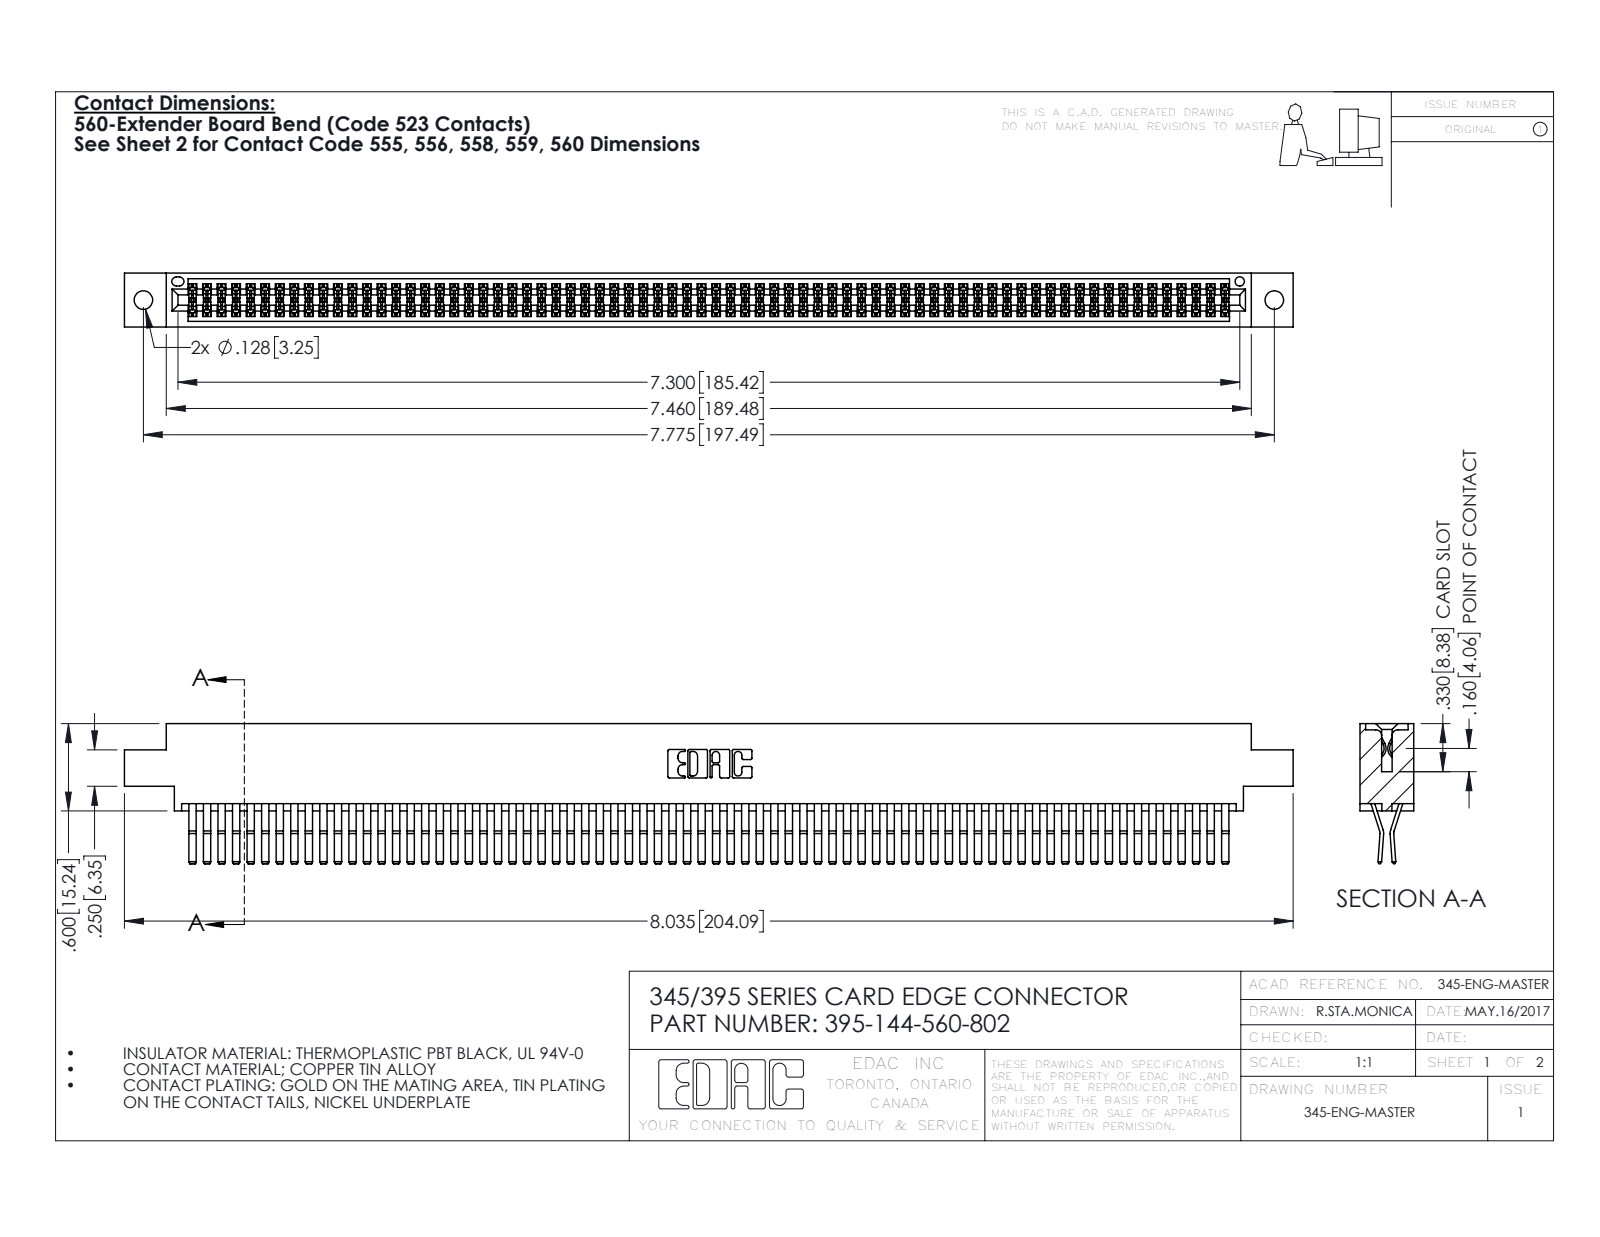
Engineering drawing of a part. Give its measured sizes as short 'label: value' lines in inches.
name: 345-292-001_560 Tail; 345 Part_0.170 Offset - 0.128 Dia; 395-144-560-802
written by: SolidWorks 2016 (CONFIG_CONTROL_DESIGN)
unit: in
bodies: 145 solids, 7618 faces (4836 planar, 2782 cylindrical, 0 other)
size: 8.035 × 0.962 × 0.37
volume: 1.275 in³; area: 52.34 in²
holes: 2× ⌀0.128, 1× ⌀0.064
rounds: 216× R0.006, 22× R0.01, 6× R0.007, 6× R0.031, 3× R0.026, 2× R0.01, 2× R0.014, 2× R0.019
face distances: 0.025, 0.298, 0.072, 0.37, 0.2, 0.098, 0.272, 0.225, 0.175, 0.149
hole spacings: 0.27, 7.539, 7.775
